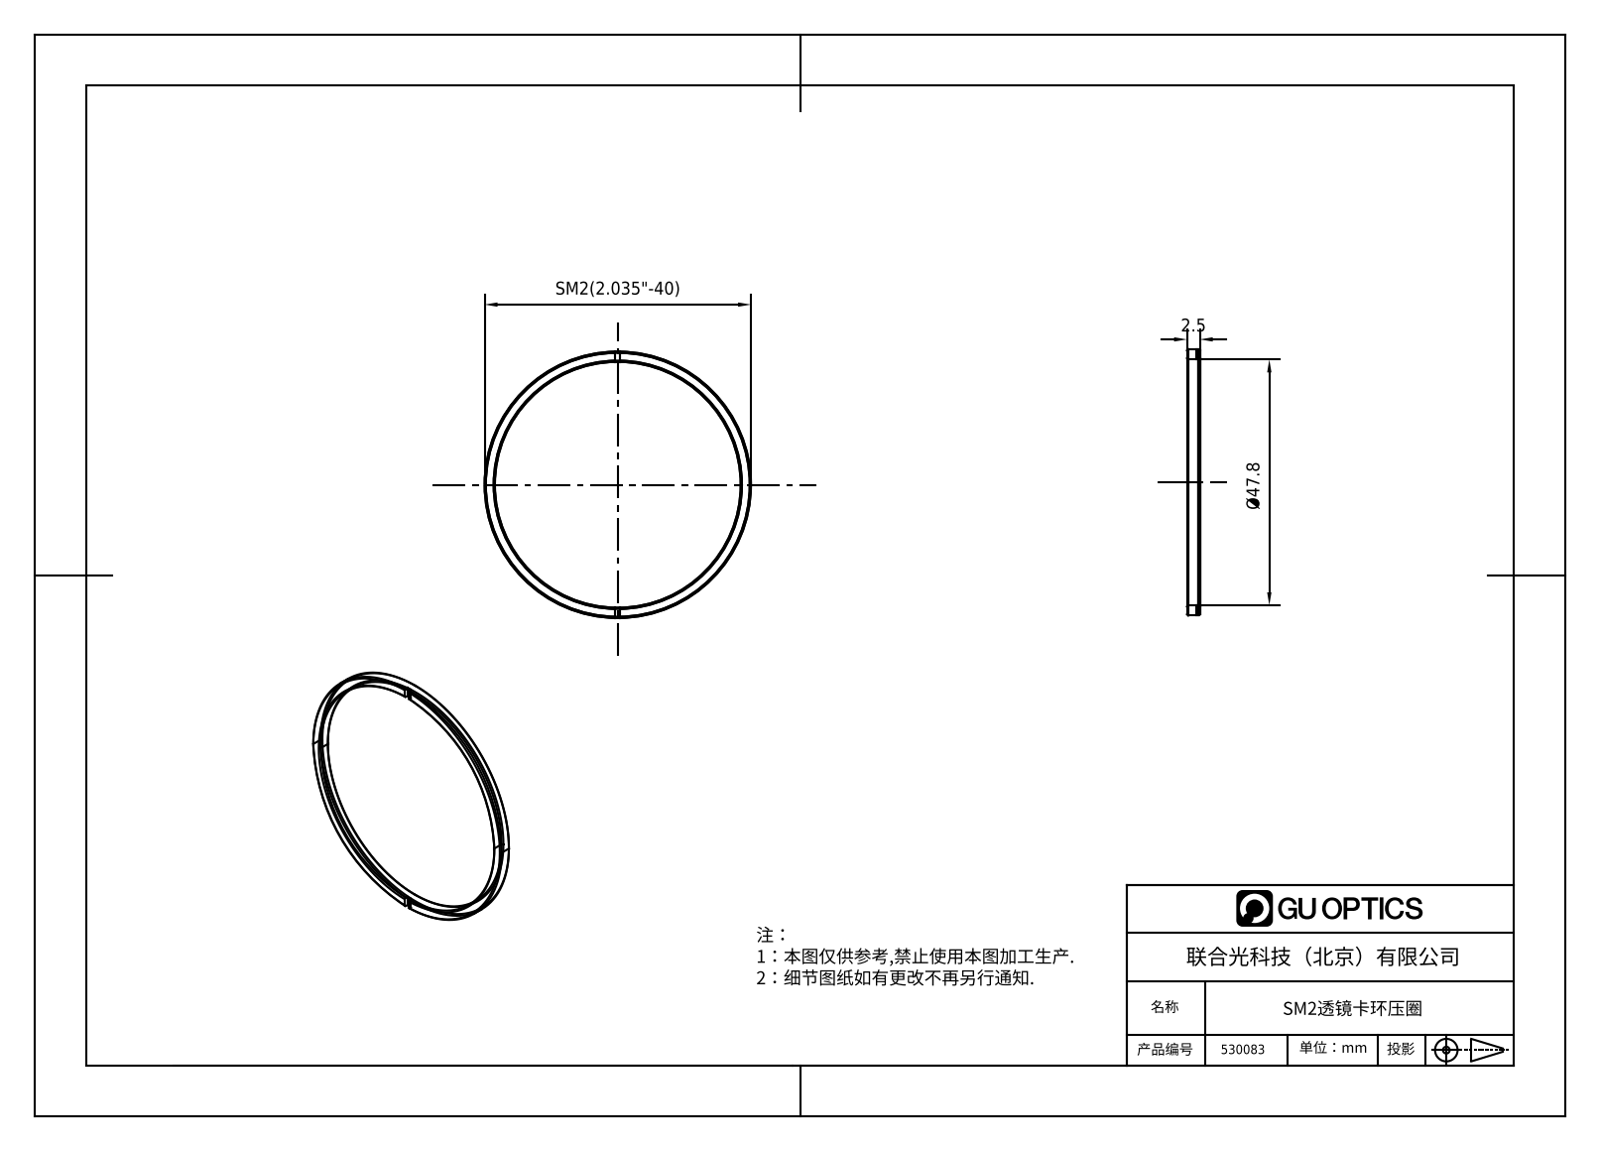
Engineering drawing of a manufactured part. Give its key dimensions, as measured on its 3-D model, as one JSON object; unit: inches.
{"part_name": "530083", "step_written_by": "SolidWorks 2020 (CONFIG_CONTROL_DESIGN)", "units": "inches", "bodies": {"solids": 1, "faces": 17, "planar": 9, "cylindrical": 2, "other": 6}, "overall_size": [2.035, 2.035, 0.098], "volume_in3": 0.039, "surface_area_in2": 1.903, "round_holes": [[1.902, 1]], "round_bosses_or_shafts": [[2.035, 1]], "face_to_face_distances": [0.098, 0.063, 0.035, 0.047]}
